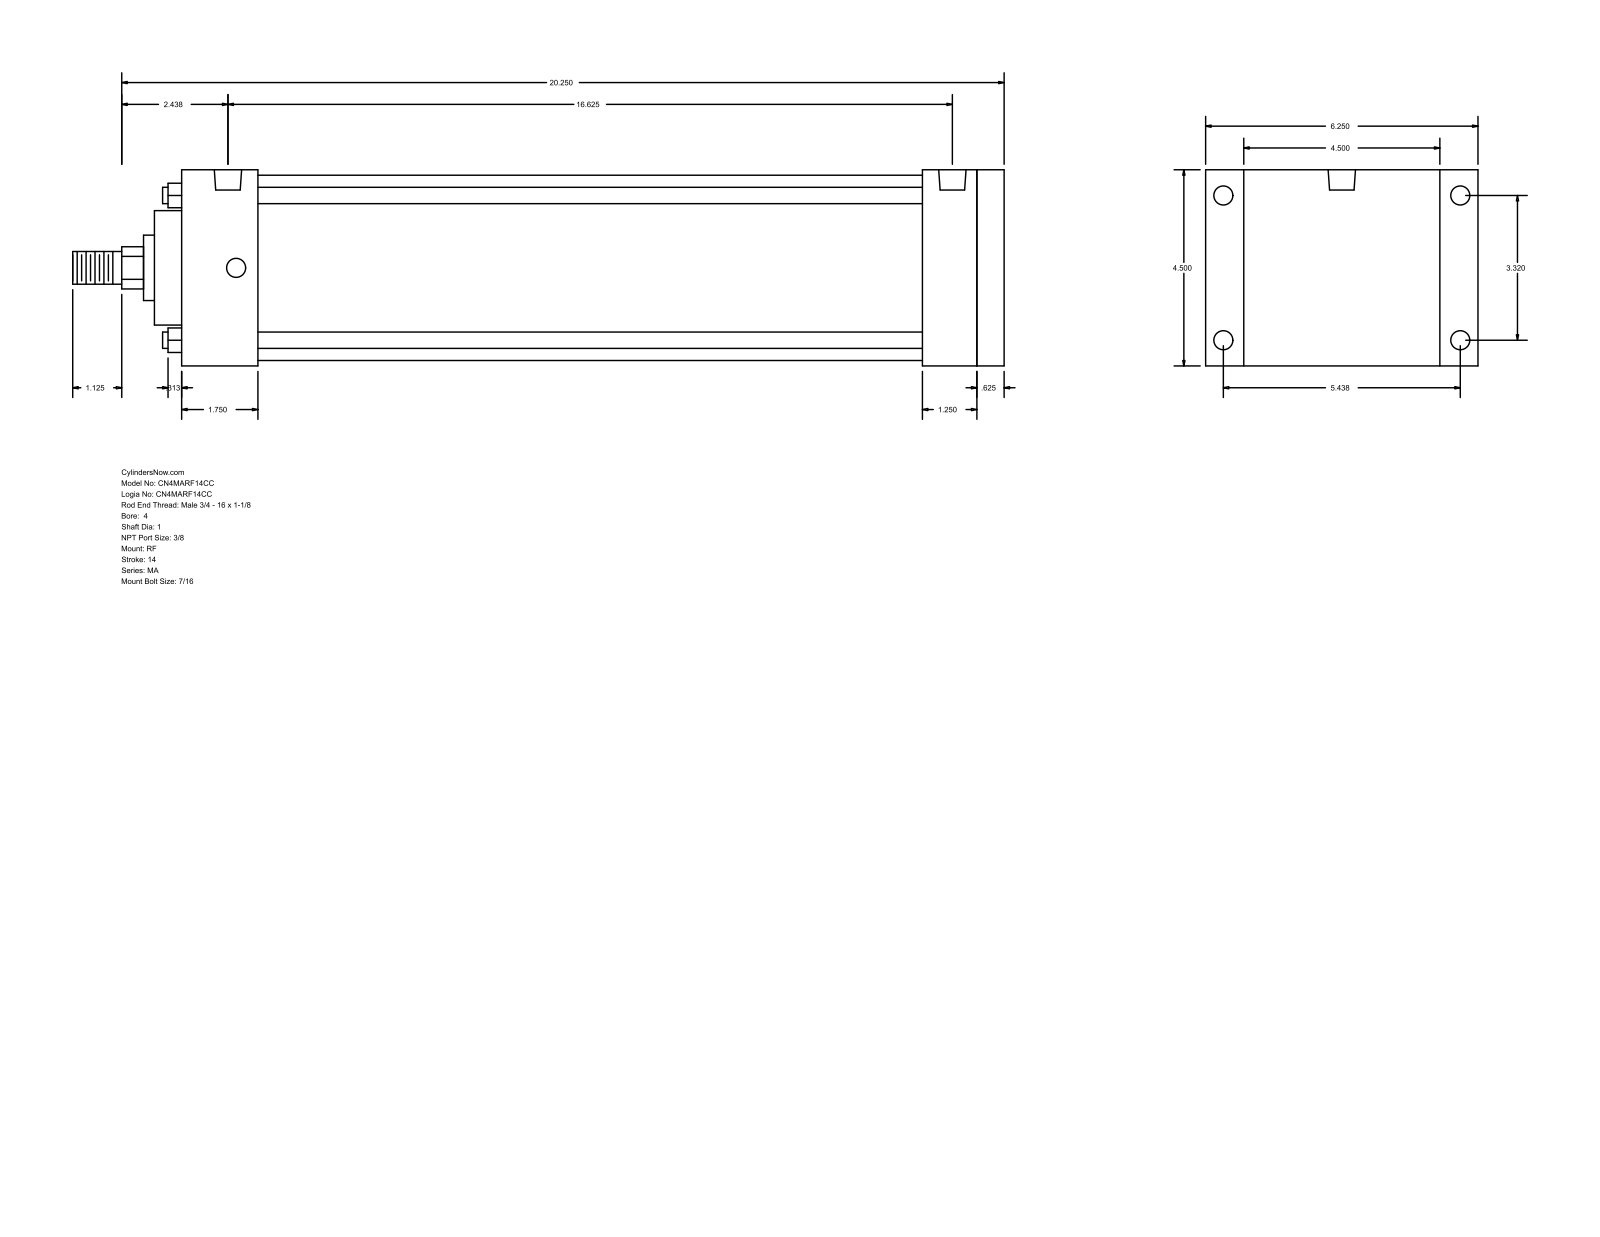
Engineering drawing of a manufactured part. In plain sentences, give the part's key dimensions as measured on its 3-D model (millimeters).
The part is named "MA_RF__0400_1". Its 3-D file was written by "GSSL Pune (CONFIG_CONTROL_DESIGN)". It is 0 solids with 94 faces: 65 planar, 29 cylindrical and 0 other. Overall it measures 542.92 by 158.75 by 114.3 millimeters. Round holes: 8 of diameter 11.11, 2 of diameter 15.93. Round bosses or shafts: 4 of diameter 9.53, 1 of diameter 107.95, 1 of diameter 66.67, 1 of diameter 38.1, 1 of diameter 25.4, 1 of diameter 19.05. Partial cylindrical surfaces (rounded edges, fillets, slot ends): 1 of radius 12.29. The main face-to-face distances are 114.3, 479.43, 15.87, 463.56, 47.62, 22.23, 136.53, 431.81, 31.75, 44.46. The hole center spacings are 4.76, 84.32, 138.12, 161.82, 412.76, 417.52, 422.28.
